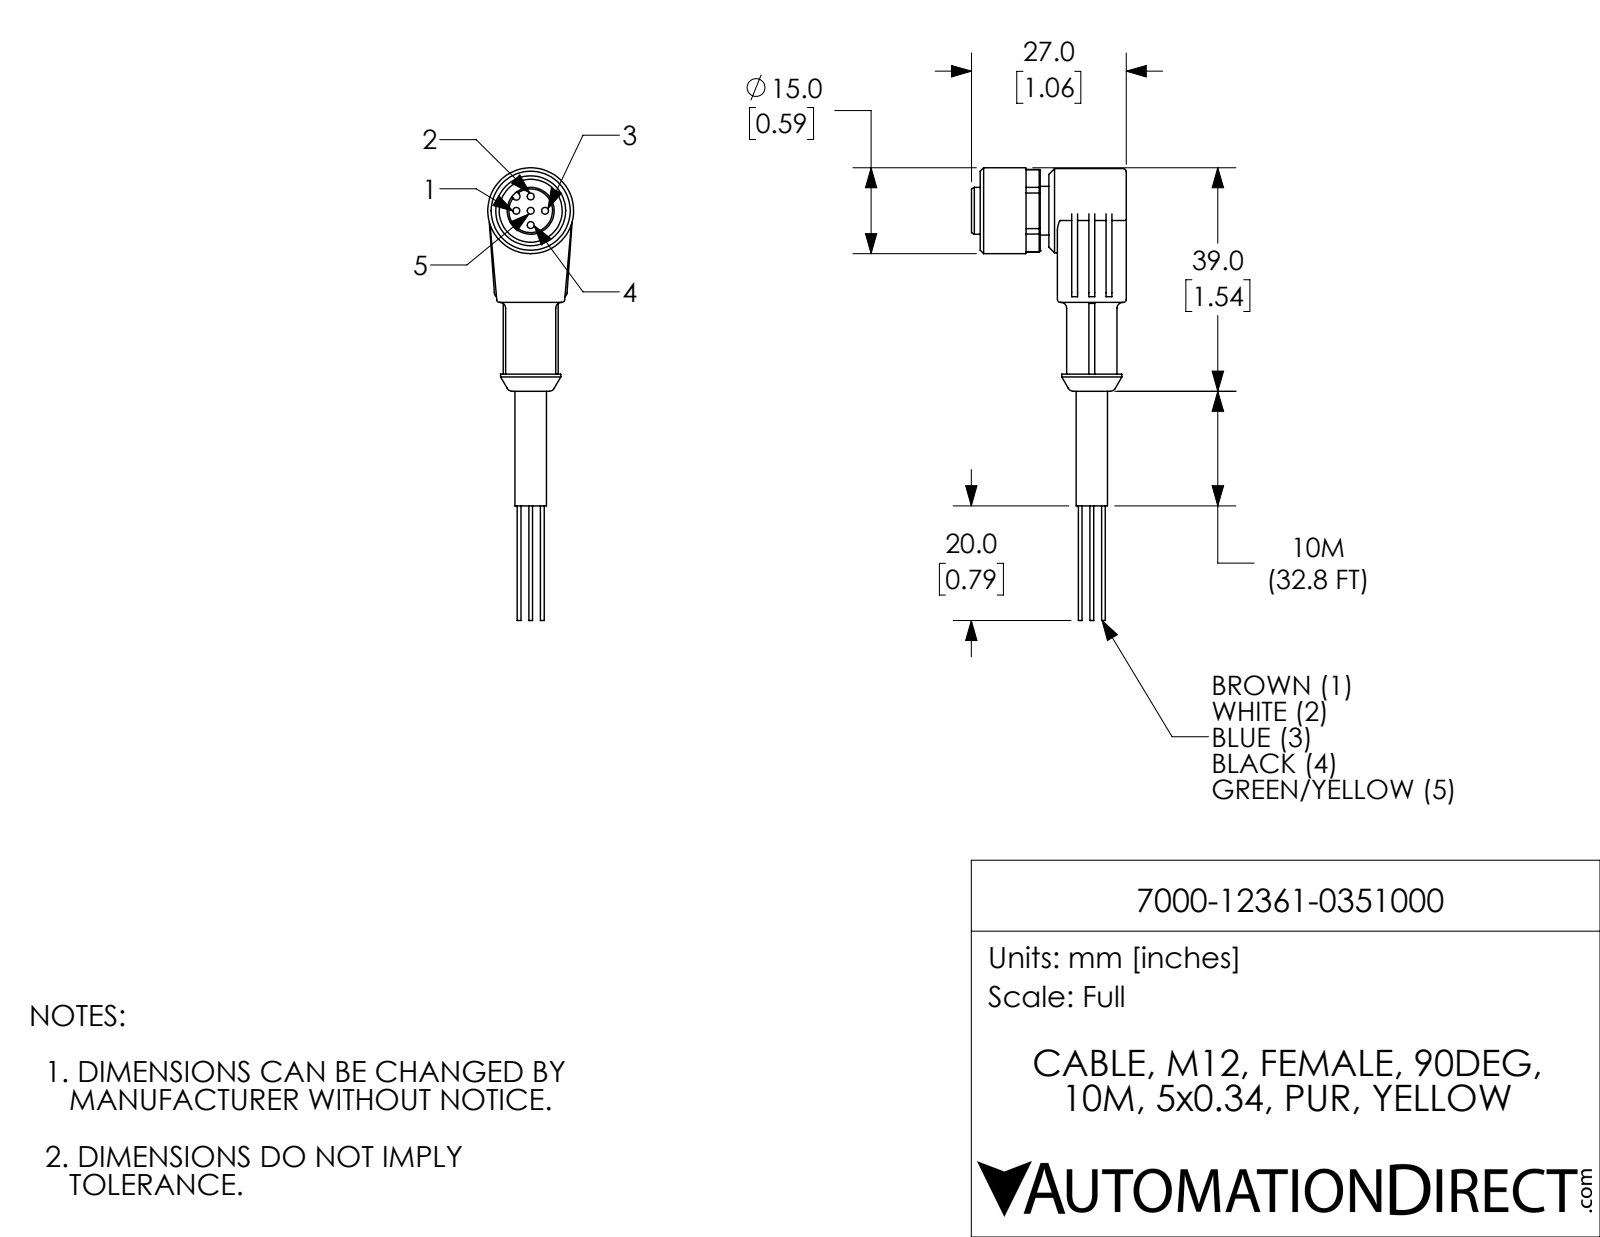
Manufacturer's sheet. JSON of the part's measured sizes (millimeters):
{"part_name": "7000-12361-0351000", "step_written_by": "SolidWorks 2021 (CONFIG_CONTROL_DESIGN)", "units": "millimeters", "bodies": {"solids": 1, "faces": 155, "planar": 66, "cylindrical": 61, "other": 28}, "overall_size": [79, 27, 15], "volume_mm3": 6830, "surface_area_mm2": 3817, "round_holes": [[1.2, 5], [4.8, 1], [11, 1]], "round_bosses_or_shafts": [[0.7, 5], [15, 1], [14.7, 1], [10.5, 1], [8.8, 1], [8.5, 1], [8.2, 1], [5.5, 1]], "partial_cylinders_radius": [[0.5, 8], [1, 2], [0.7, 1], [7.2, 1]], "face_to_face_distances": [12, 1.5, 3, 13.5, 15, 5.5, 9.5, 6, 8, 12.5], "hole_center_spacings": [2.5, 3.5, 5]}
